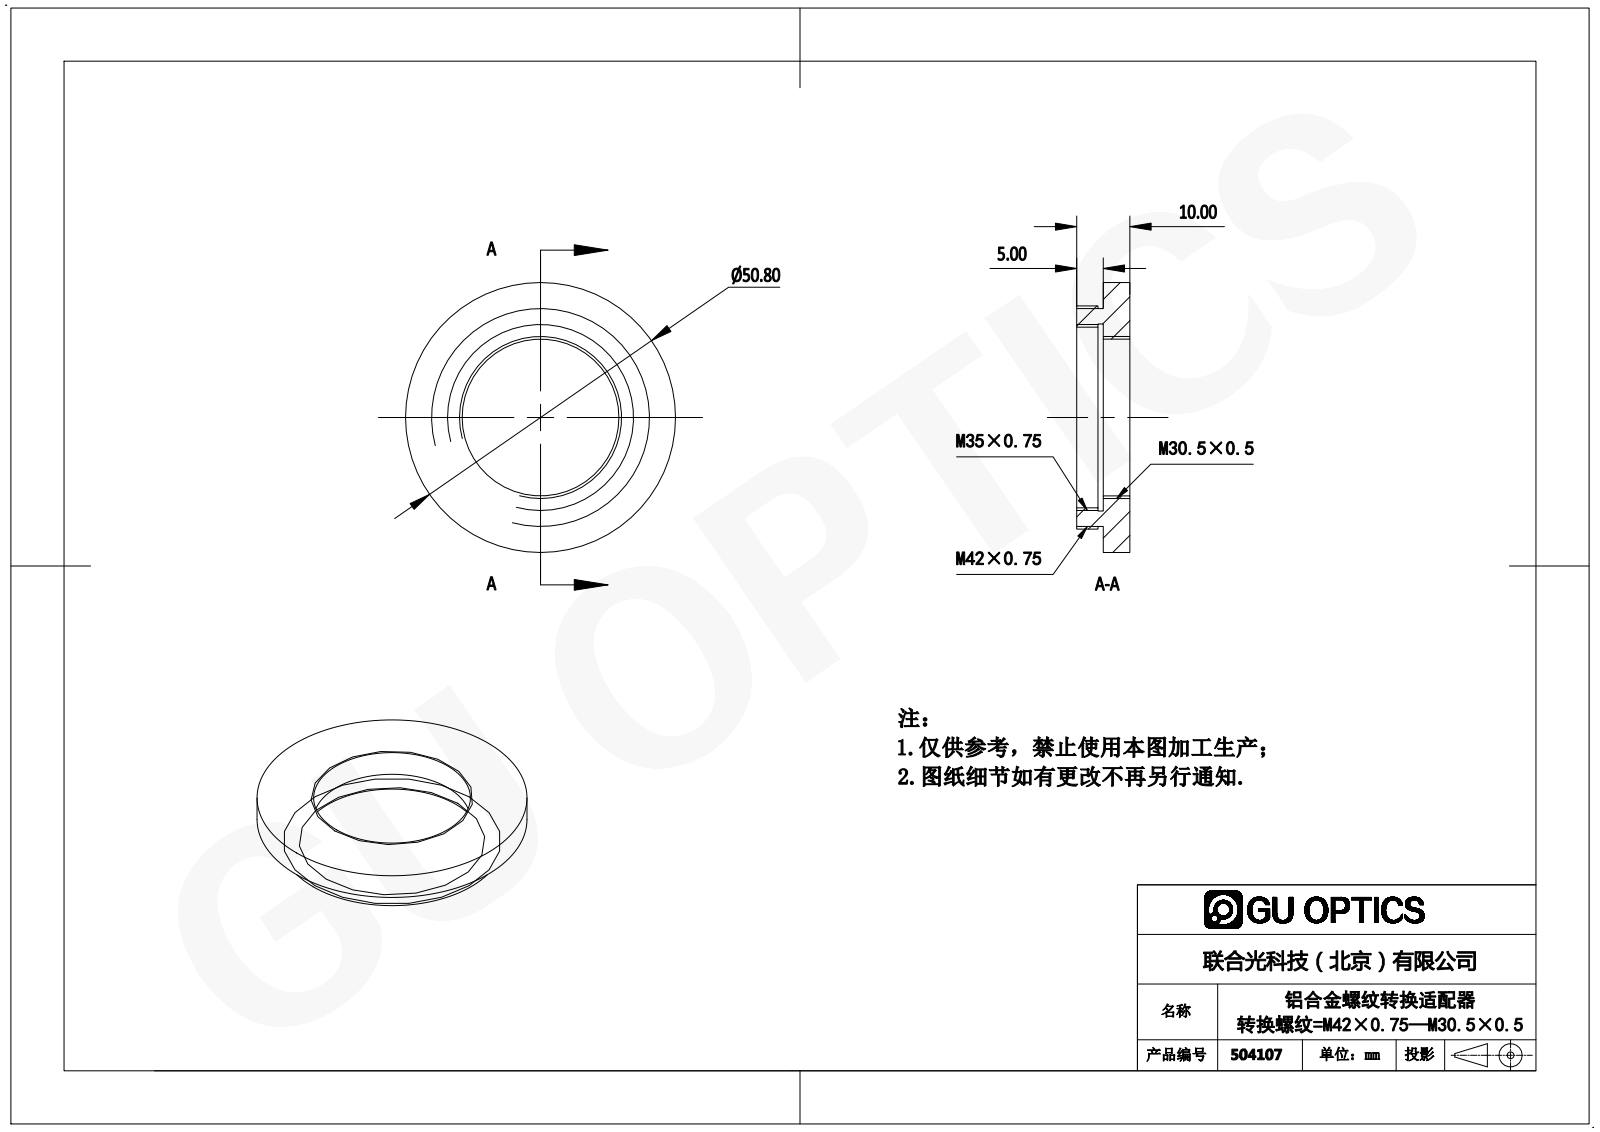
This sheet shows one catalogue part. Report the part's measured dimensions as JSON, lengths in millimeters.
{"part_name": "504107", "step_written_by": "SolidWorks 2016 (AUTOMOTIVE_DESIGN)", "units": "millimeters", "bodies": {"solids": 1, "faces": 18, "planar": 6, "cylindrical": 12, "other": 0}, "overall_size": [50.8, 50.8, 10], "volume_mm3": 8974, "surface_area_mm2": 5403, "round_holes": [[29.5, 1], [34, 1], [35.2, 1]], "round_bosses_or_shafts": [[50.8, 1], [42, 1], [41, 1]], "face_to_face_distances": [5, 10, 4, 1, 6]}
